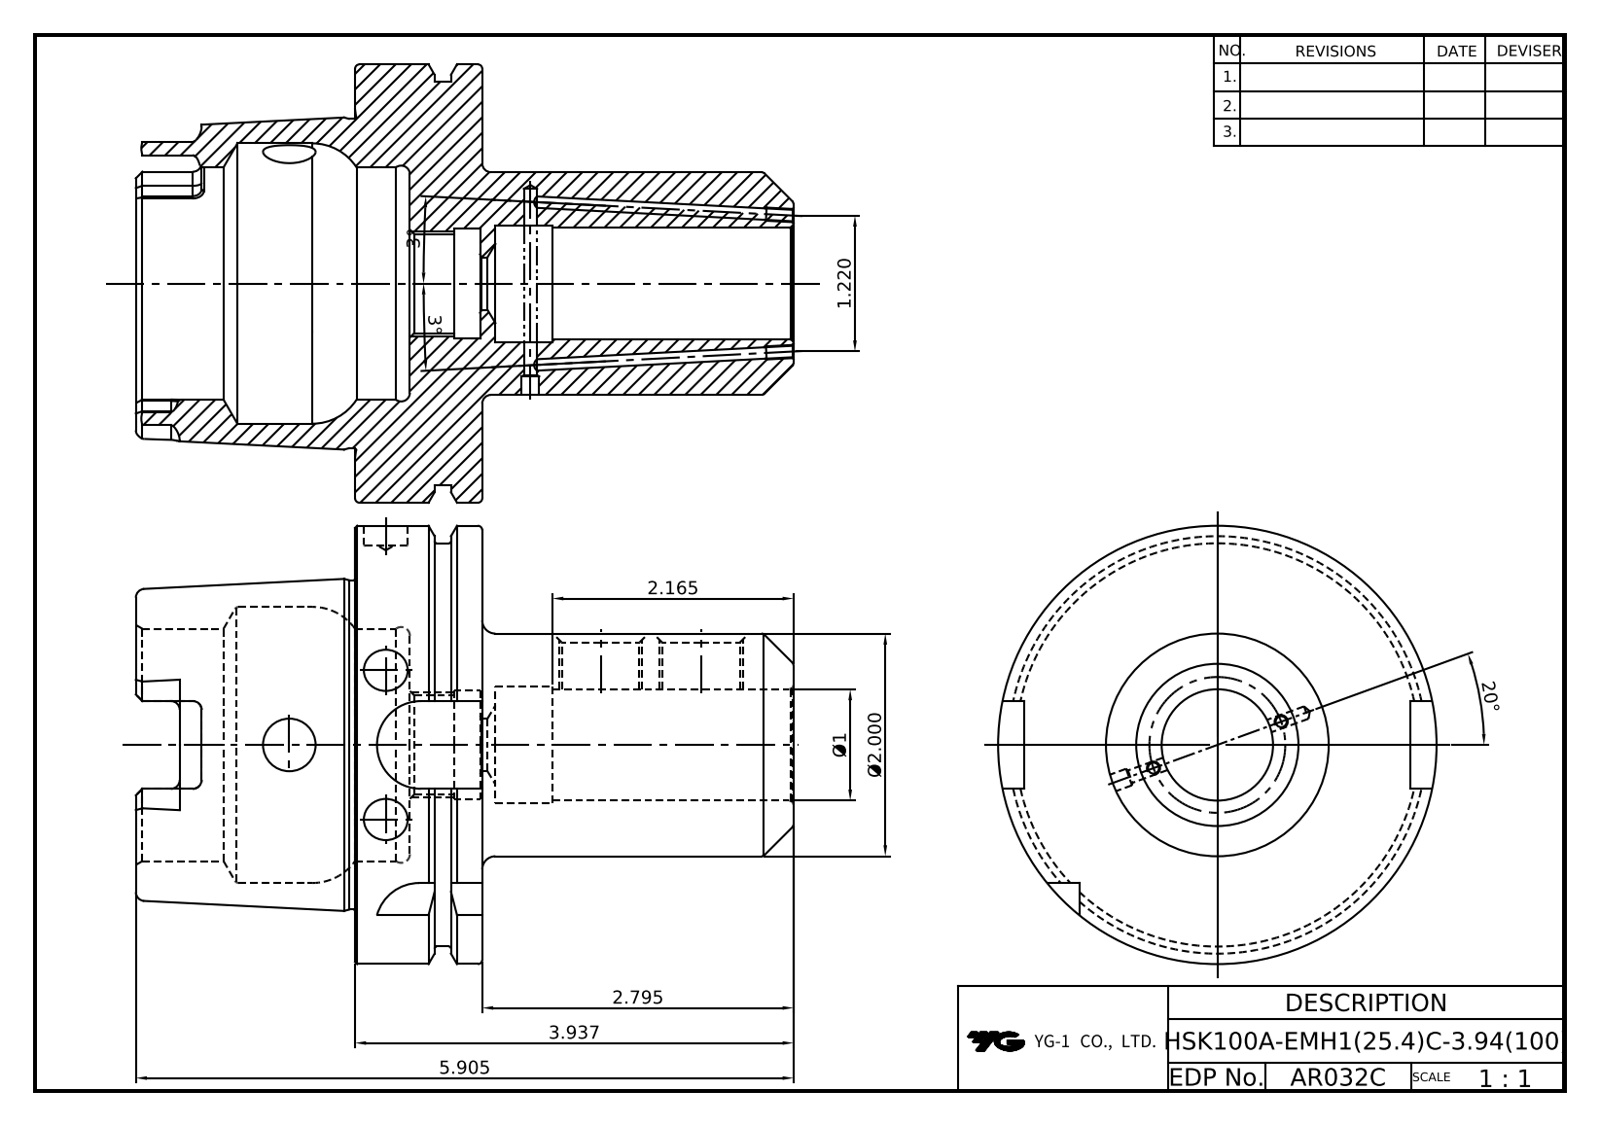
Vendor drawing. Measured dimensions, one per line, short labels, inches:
name: LO-HSK100A-EMH25.4C-100
written by: Autodesk Inventor 2022 (AUTOMOTIVE_DESIGN)
unit: in
bodies: 1 solid, 135 faces (42 planar, 43 cylindrical, 50 other)
size: 5.906 × 3.937 × 3.937
volume: 21.45 in³; area: 104.5 in²
holes: 3× ⌀0.394, 2× ⌀0.097, 2× ⌀0.472, 2× ⌀0.682, 1× ⌀0.118, 1× ⌀0.157, 1× ⌀0.881, 1× ⌀0.984, 1× ⌀1, 1× ⌀1.047, 1× ⌀2.087, 1× ⌀2.48
bosses: 1× ⌀3.937, 1× ⌀3.622, 1× ⌀2.969, 1× ⌀2
rounds: 6× R0.079, 4× R0.192, 4× R0.394
face distances: 1.142, 0.492, 0.65, 2.461, 1.969, 3.11, 3.228, 1.26, 0.768, 0.118
hole spacings: 1.299, 0.902, 1.929, 2.831
